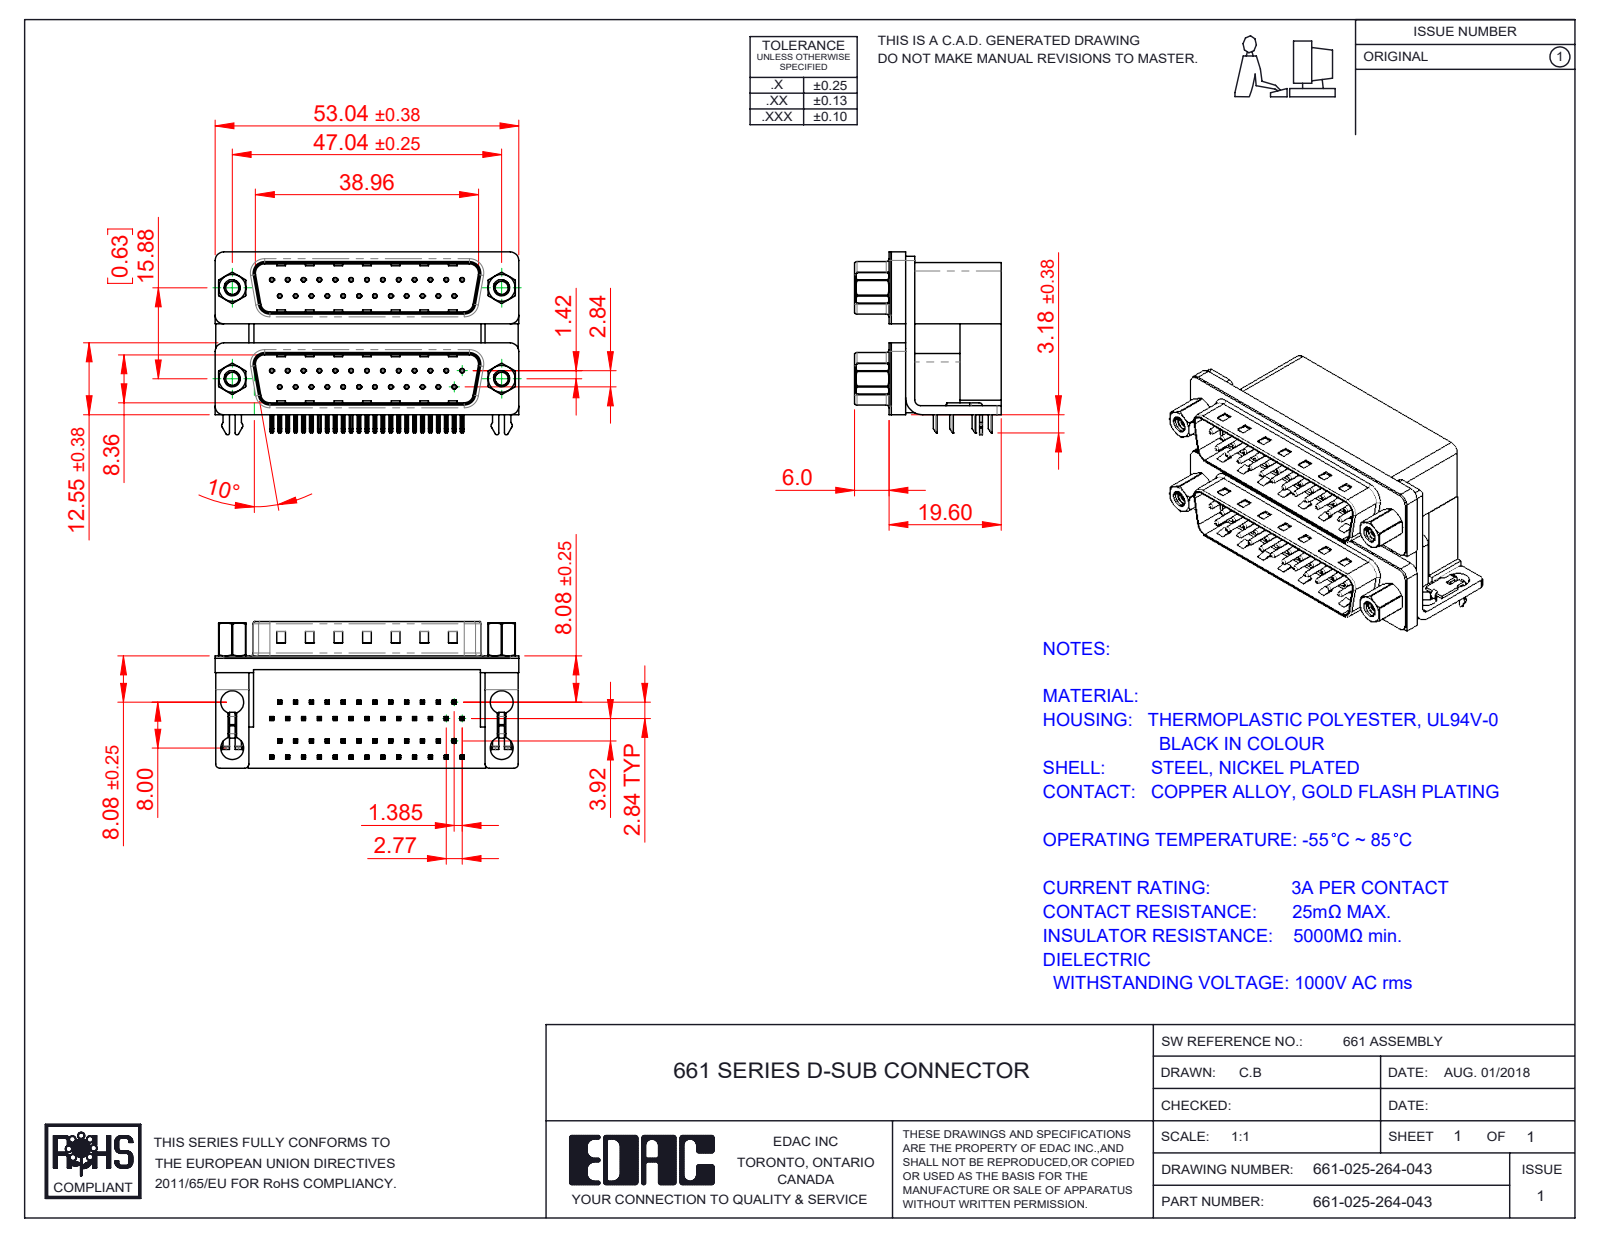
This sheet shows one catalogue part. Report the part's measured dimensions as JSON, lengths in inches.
{"part_name": "661 Shell_25 Contacts; 661 Contact Bottom Lower; 661 Threaded Rivet_4-40; 661-025-264-043 (+8 more)", "step_written_by": "SolidWorks 2020 (CONFIG_CONTROL_DESIGN)", "units": "inches", "bodies": {"solids": 69, "faces": 5058, "planar": 3078, "cylindrical": 1490, "other": 490}, "overall_size": [2.088, 1.249, 1.008], "volume_in3": 1.267, "surface_area_in2": 35.02, "round_holes": [[0.014, 50], [0.031, 50], [0.079, 4], [0.089, 4], [0.09, 4], [0.098, 4], [0.126, 4], [0.138, 4], [0.157, 4], [0.189, 4], [0.197, 4]], "round_bosses_or_shafts": [[0.03, 50], [0.193, 4], [0.187, 4], [0.157, 4], [0.154, 4], [0.134, 4], [0.13, 4], [0.114, 4]], "partial_cylinders_radius": [[0.01, 200], [0.005, 100], [0.02, 16], [0.059, 13], [0.03, 8], [0.035, 8], [0.063, 8], [0.079, 8]], "face_to_face_distances": [0.016, 0.756, 0.283, 0.472, 0.421, 0.625, 0.657, 0.374, 0.098, 0.611], "hole_center_spacings": [0.124, 0.109, 0.218, 0.327, 0.436, 0.545, 0.654, 0.198]}
